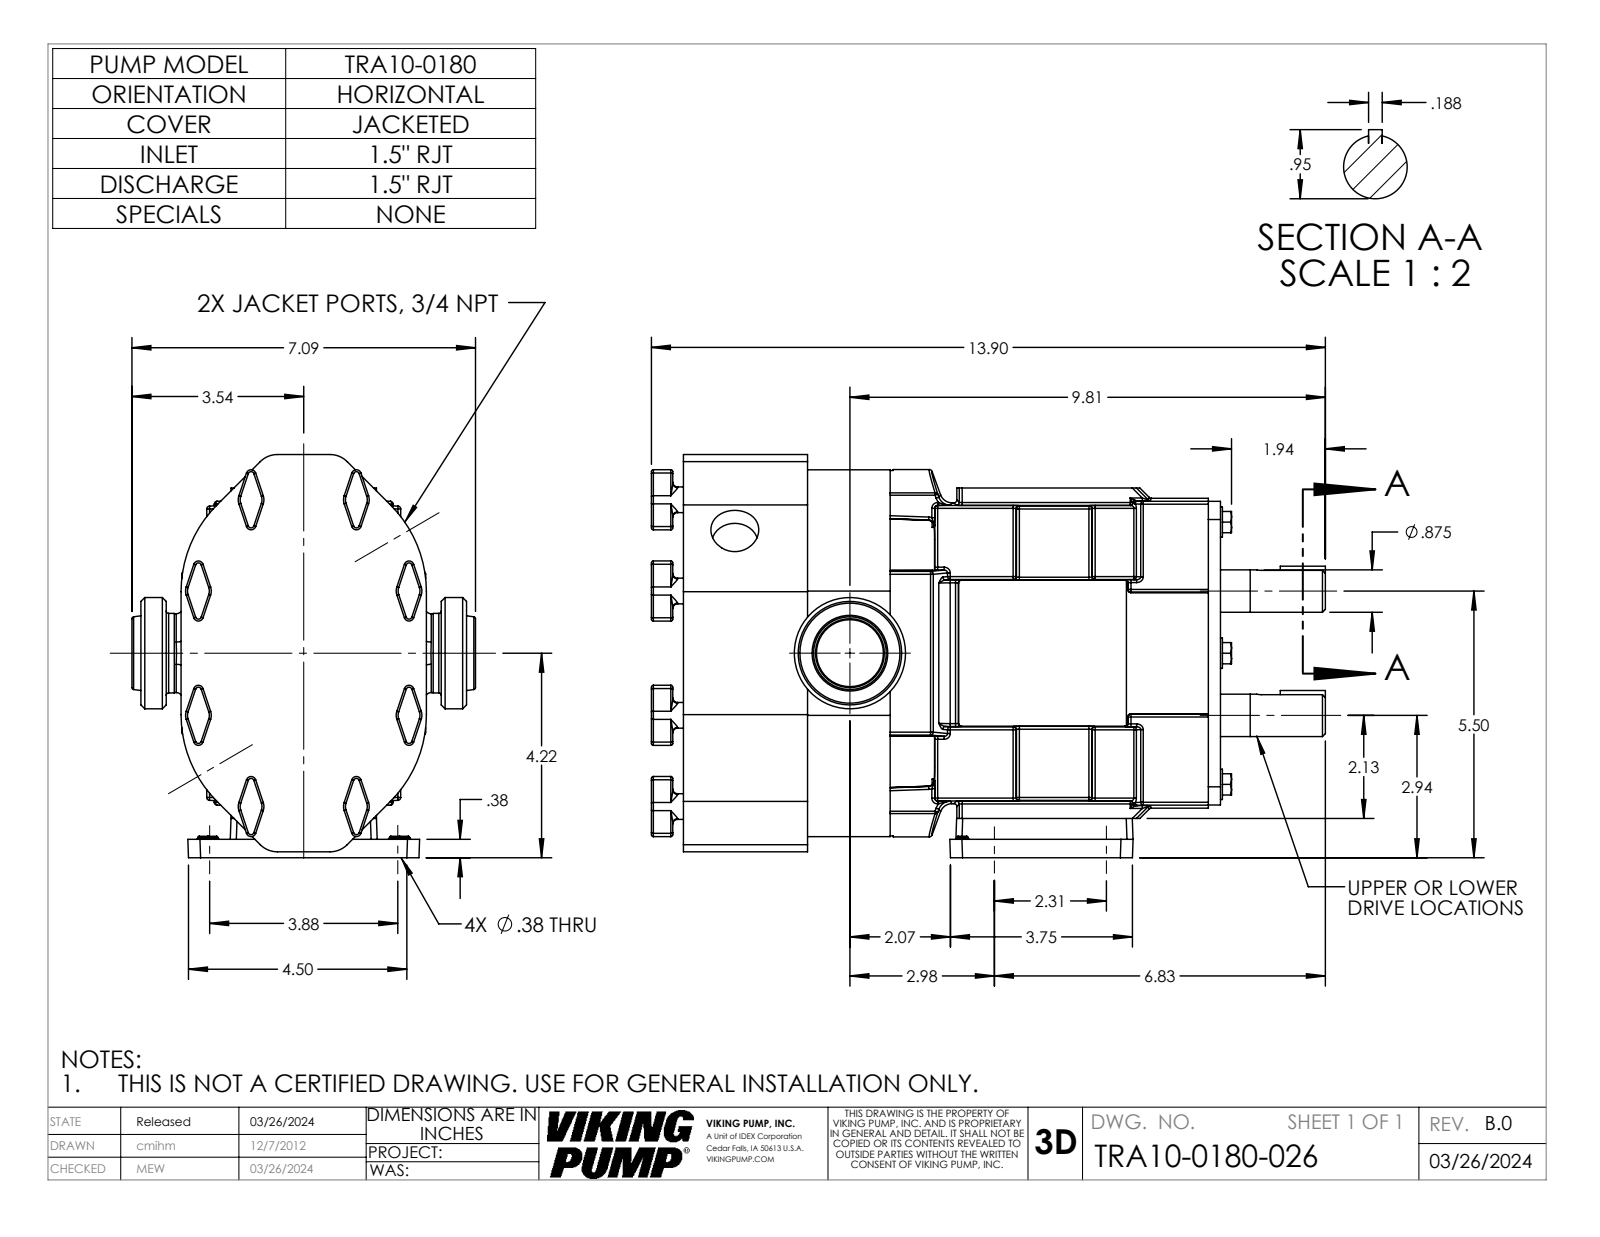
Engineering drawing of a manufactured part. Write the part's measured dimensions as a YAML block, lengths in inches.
part_name: "TRA10-0150-GEARBOX-H; TRA10-0180-026; TRA10-0180-BODY; 0300RJT15 (+1 more)"
step_written_by: "SolidWorks 2022 (AUTOMOTIVE_DESIGN)"
units: inches
bodies: {solids: 5, faces: 1173, planar: 320, cylindrical: 445, other: 408}
overall_size: [13.9, 8.313, 7.086]
volume: 310.3
surface_area: 545.8
round_holes:
  - {diameter: 0.375, count: 4}
  - {diameter: 1.38, count: 1}
  - {diameter: 1.406, count: 1}
  - {diameter: 2.063, count: 1}
round_bosses_or_shafts:
  - {diameter: 0.53, count: 8}
  - {diameter: 0.625, count: 6}
  - {diameter: 0.874, count: 2}
  - {diameter: 2.294, count: 1}
  - {diameter: 1.64, count: 1}
  - {diameter: 1.625, count: 1}
partial_cylinders:
  - {radius: 0.06, count: 181}
  - {radius: 0.04, count: 64}
  - {radius: 0.125, count: 20}
  - {radius: 0.03, count: 16}
  - {radius: 0.1, count: 16}
  - {radius: 0.25, count: 14}
  - {radius: 0.375, count: 4}
  - {radius: 0.5, count: 4}
face_to_face_distances: [1.704, 2.56, 4.264, 11.077, 8.517, 6.813, 5.389, 2.829, 1.125, 5.687]
hole_center_spacings: [2.31, 3.88, 4.516]
